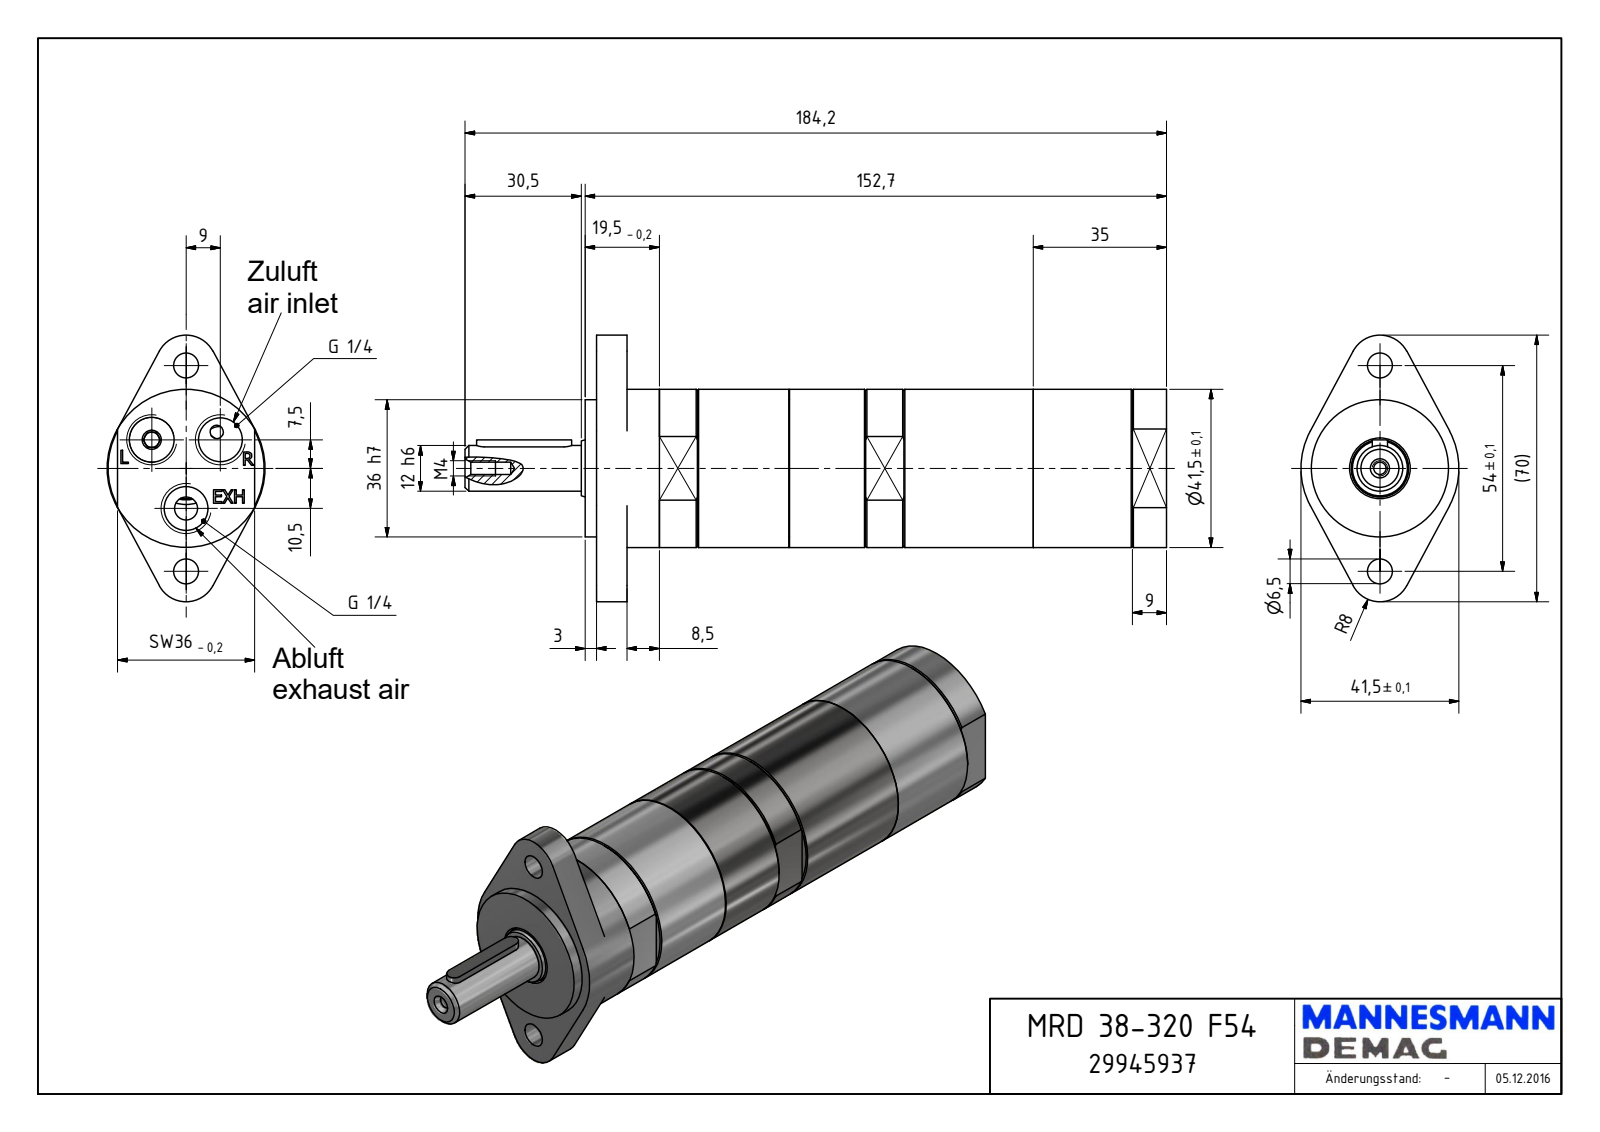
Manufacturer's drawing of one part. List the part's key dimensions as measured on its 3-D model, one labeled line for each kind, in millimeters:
Part name (STEP PRODUCT): MRD 38-320 F70_29945937
STEP written by: Autodesk Inventor 2018 (AUTOMOTIVE_DESIGN)
Units: millimetres
Bodies: 1 solid, 165 faces (109 planar, 27 cylindrical, 29 other)
Overall size (bounding box): 184.2 × 70 × 41.5
Volume: 208 442 mm³ · Surface area: 27 885 mm²
Round holes (diameter × count): ⌀11.45 ×3, ⌀6.5 ×2, ⌀3.24 ×1, ⌀4 ×1, ⌀16 ×1
Round bosses / shafts (diameter × count): ⌀41.5 ×1, ⌀36 ×1, ⌀14.95 ×1, ⌀12 ×1
Partial cylindrical surfaces — rounded edges, fillets, slot ends (radius × count): R2 ×2, R8 ×2
Main face-to-face distances: 149.7, 3, 152.7, 11, 8, 141.7, 1, 42.5, 41.48, 37
Hole centre spacings: 11.72, 20.12, 21.48, 27, 35.65, 10.5, 16.5, 18
